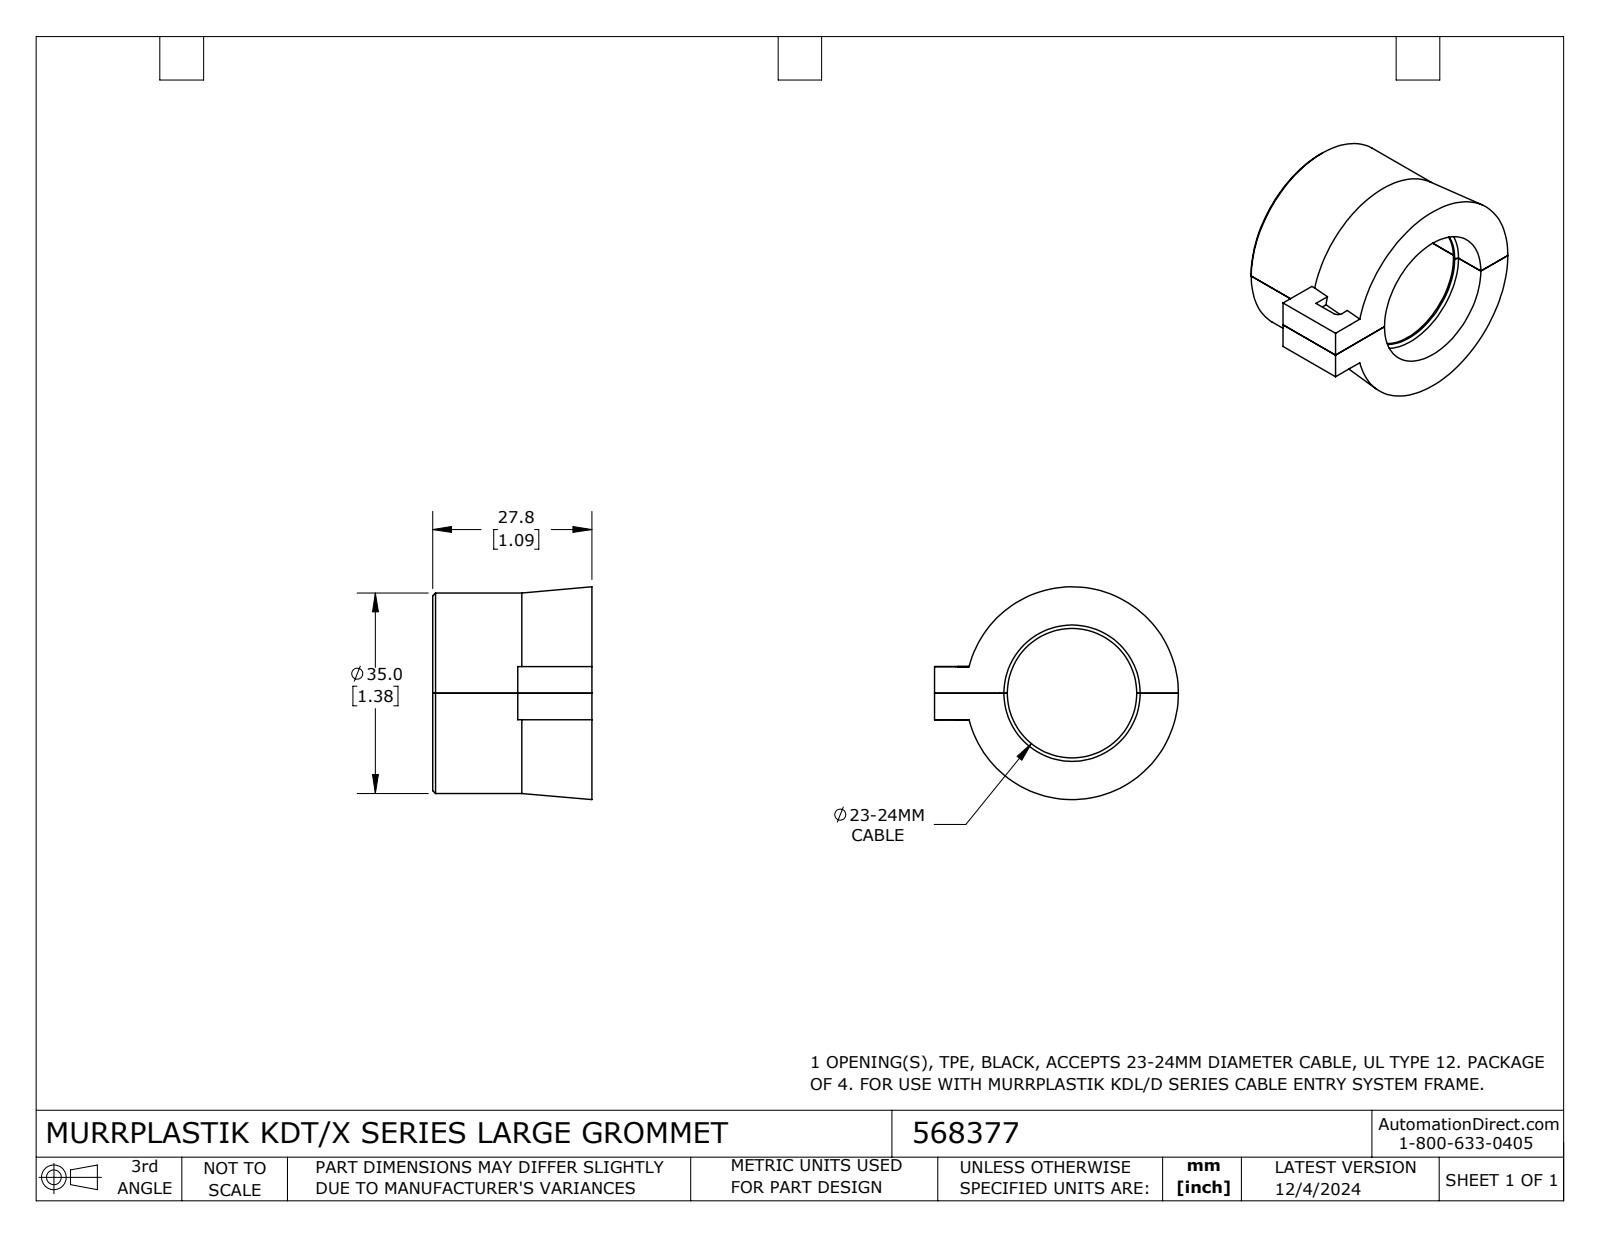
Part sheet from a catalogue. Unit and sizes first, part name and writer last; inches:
Units: inches
Overall size (bounding box): 1.676 × 1.462 × 1.094
Round holes (diameter × count): ⌀0.89 ×1, ⌀0.937 ×1
Round bosses / shafts (diameter × count): ⌀1.378 ×1
Partial cylindrical surfaces — rounded edges, fillets, slot ends (radius × count): R0.02 ×4, R0.039 ×1
Main face-to-face distances: 1.094, 0.183, 0.366, 0.51, 0.585, 0.061, 0.305, 0.122, 0.157, 0.243
Volume: 0.966 in³ · Surface area: 11.6 in²
Bodies: 2 solids, 46 faces (22 planar, 14 cylindrical, 10 other)
Part name (STEP PRODUCT): 568377
STEP written by: SolidWorks 2024 (AUTOMOTIVE_DESIGN)
